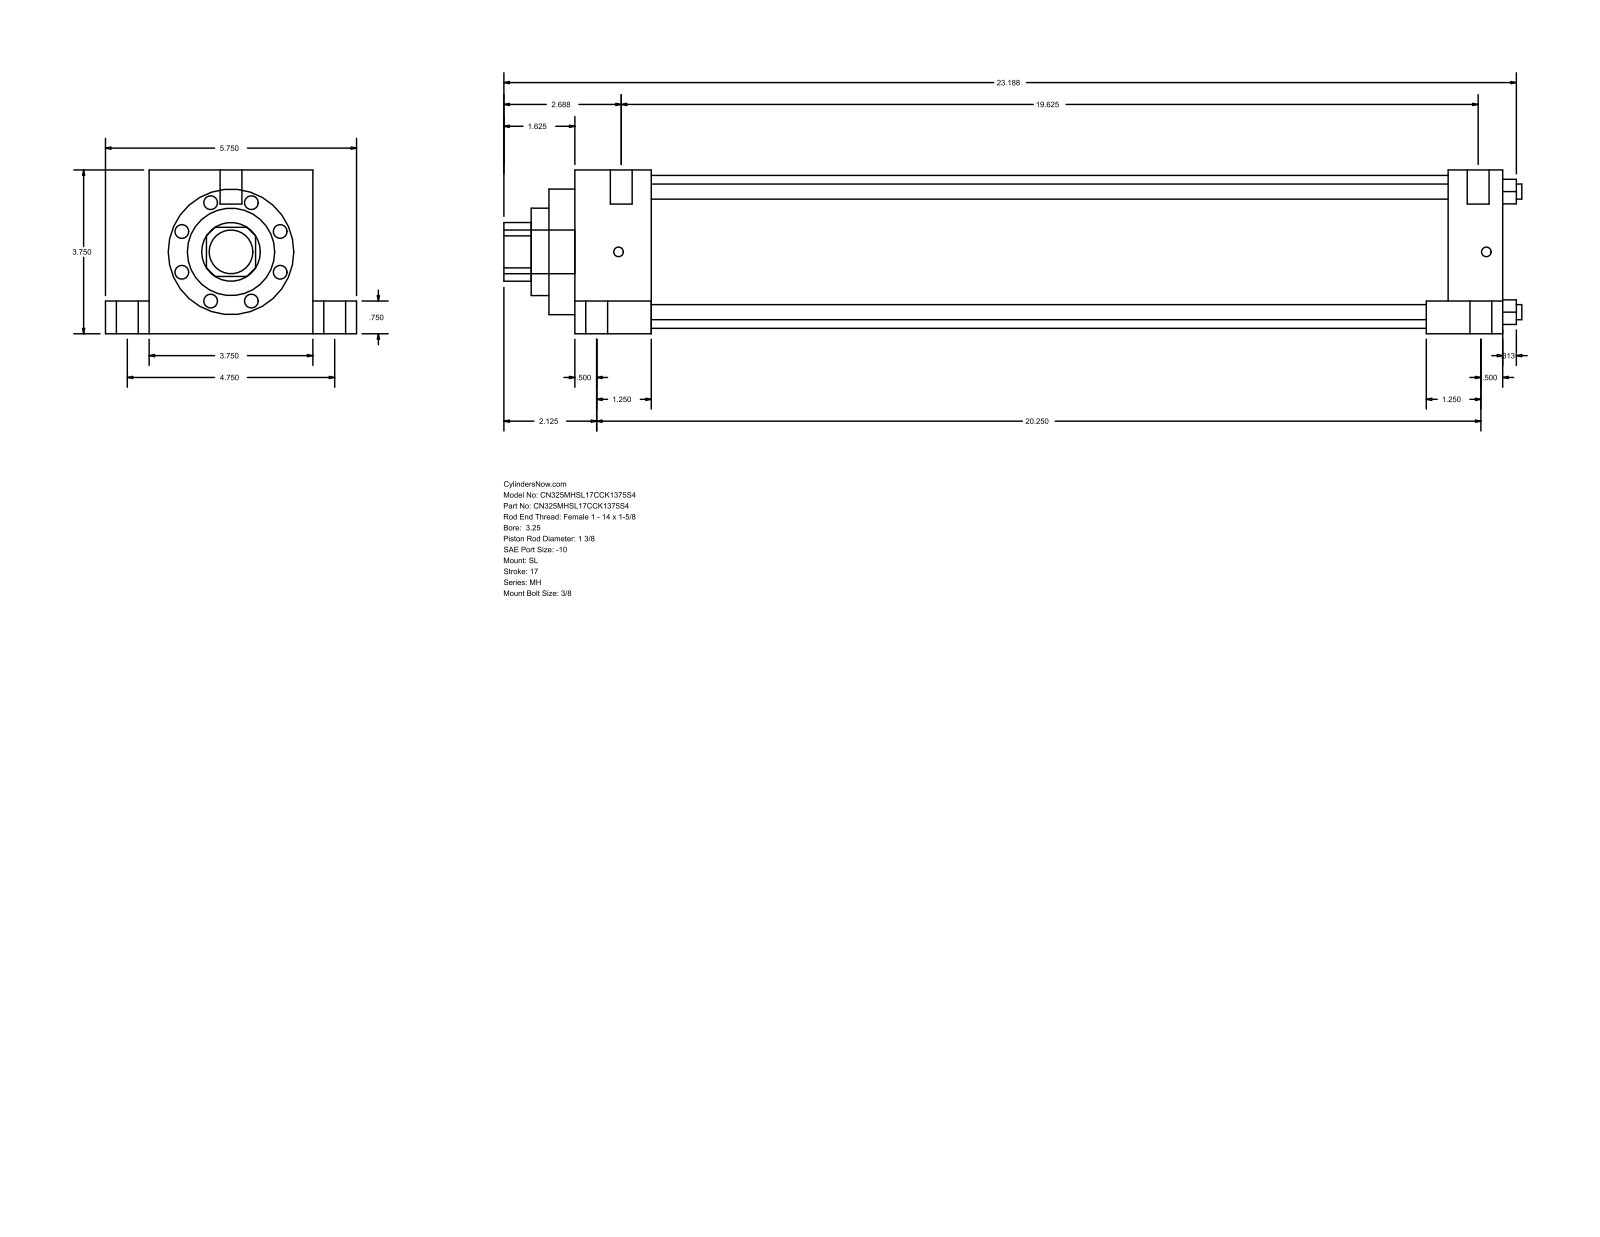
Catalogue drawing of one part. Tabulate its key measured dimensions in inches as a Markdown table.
| quantity | value |
| --- | --- |
| part name | MH_SL__0325_1.375 |
| STEP written by | GSSL Pune (CONFIG_CONTROL_DESIGN) |
| units | inches |
| bodies | 0 solids, 110 faces (77 planar, 33 cylindrical, 0 other) |
| overall size | 23.313 × 5.75 × 3.75 |
| round holes (diameter × count) | 0.345 × 4, 1.375 × 1, 2 × 1, 2.875 × 1, 3.5 × 1 |
| round bosses / shafts (diameter × count) | 0.5 × 6, 0.75 × 4, 0.219 × 4, 1 × 1 |
| partial cylindrical surfaces (radius × count) | 0.672 × 1 |
| main face-to-face distances | 3.75, 21.25, 1.75, 19.5, 1, 4.75, 0.75, 3, 20, 18.25 |
| hole center spacings | 1.952, 2.76, 3.903 |
